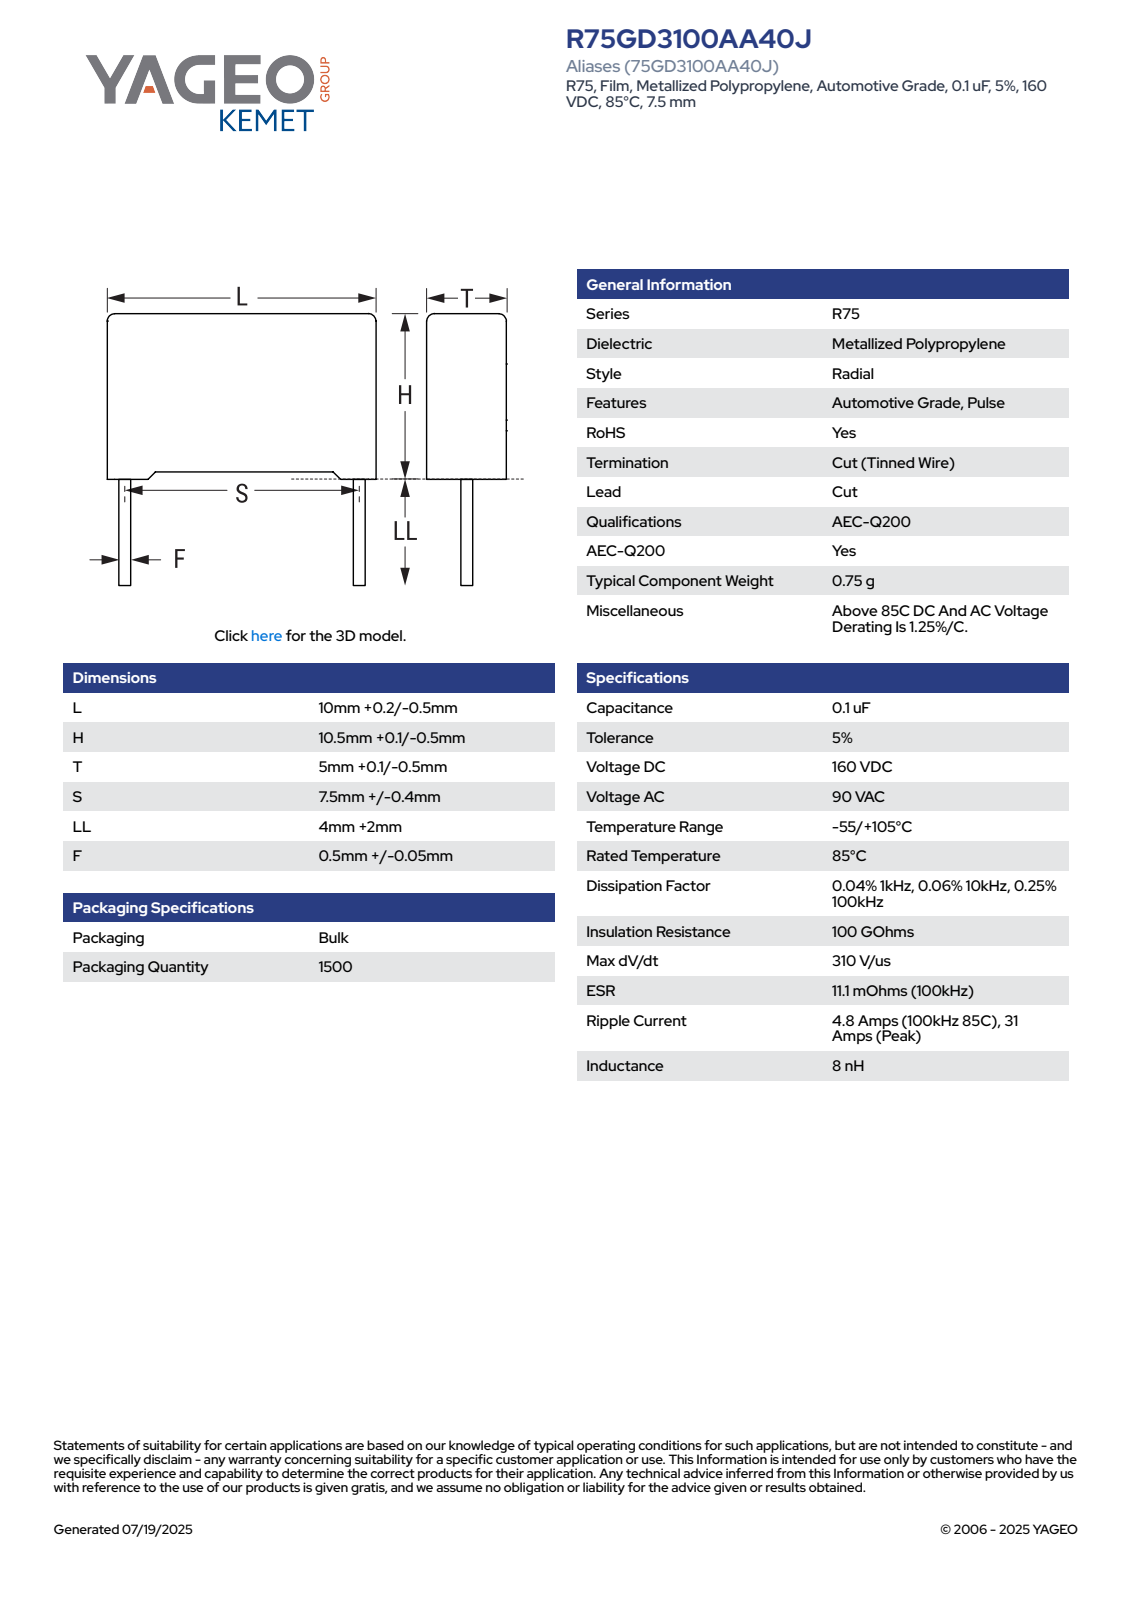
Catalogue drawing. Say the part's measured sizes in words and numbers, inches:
The part is named "CFR_RB2_10X10.5X5_L10.2H10.6T5.1S7.5LL6F0.55". Its 3-D file was written by "SolidWorks 2021 (AUTOMOTIVE_DESIGN)". It is 4 solids with 85 faces: 77 planar, 8 cylindrical and 0 other. Overall it measures 0.654 by 0.402 by 0.201 inches. Its volume is 0.032 cubic inches and its surface area 0.725 square inches. Round bosses or shafts: 2 of diameter 0.022. Partial cylindrical surfaces (rounded edges, fillets, slot ends): 4 of radius 0.02. The main face-to-face distances are 0.201, 0.402, 0.388, 0.013, 0.187, 0.03, 0.417, 0.388, 0.174, 0.375.
